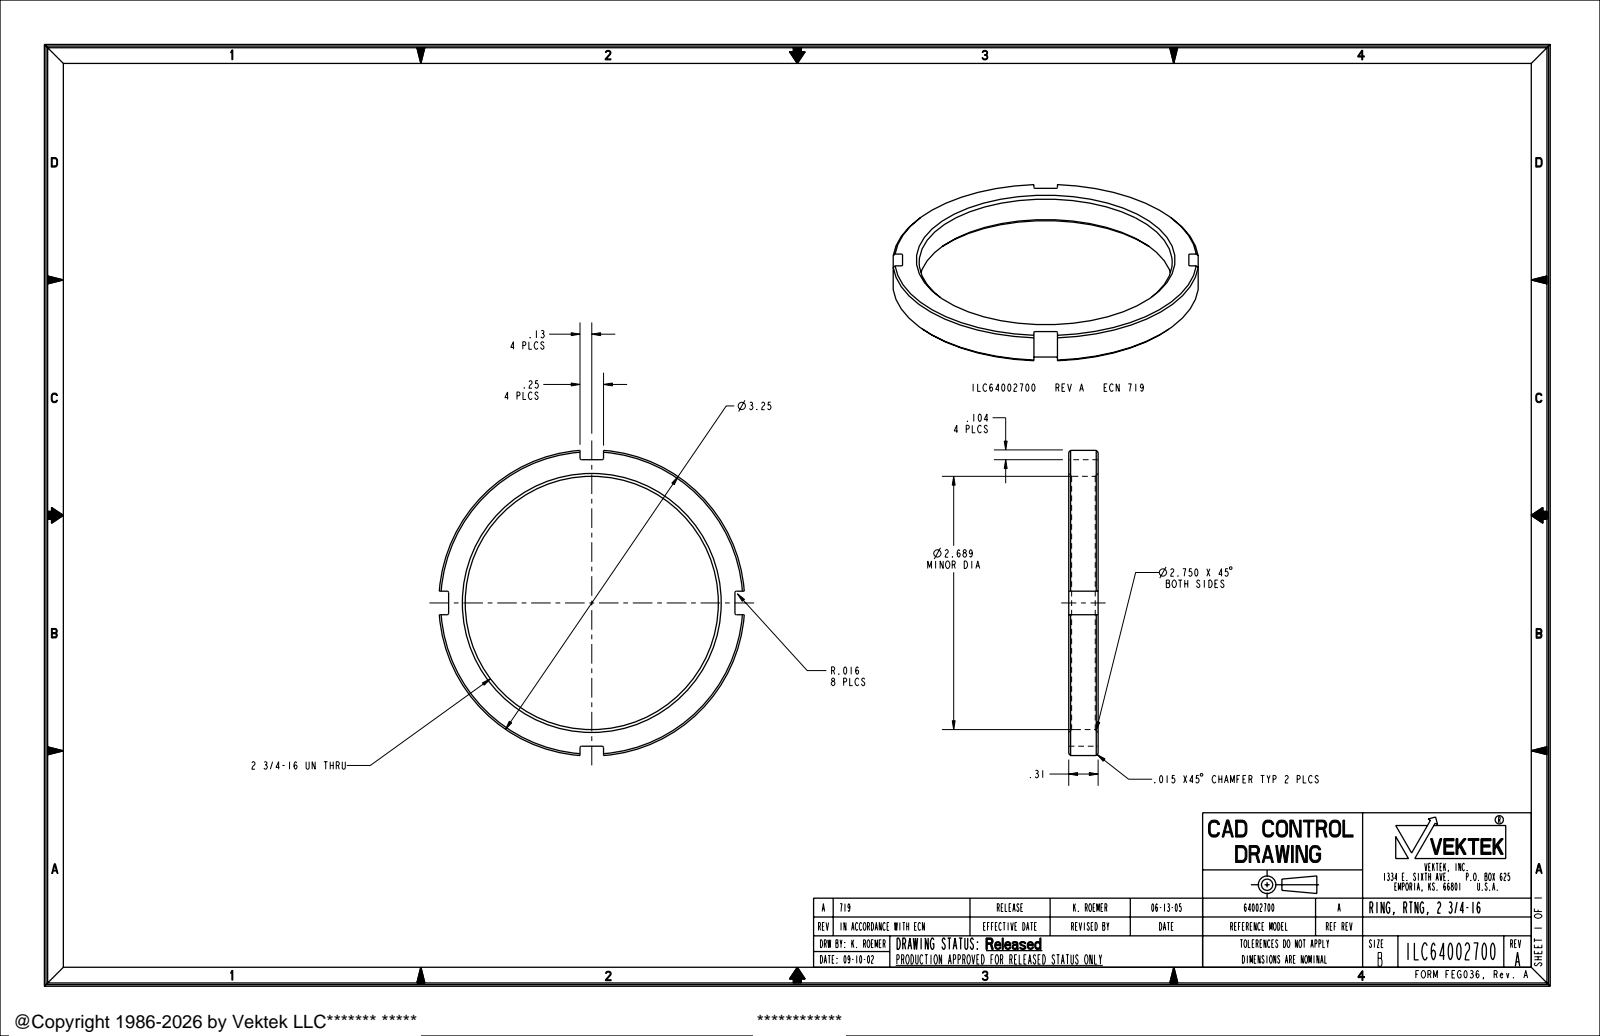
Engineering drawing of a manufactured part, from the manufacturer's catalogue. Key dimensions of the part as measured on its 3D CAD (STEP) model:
Part name (STEP PRODUCT): ILC64002700
STEP written by: PRO/ENGINEER BY PARAMETRIC TECHNOLOGY CORPORATION, 2004290 (AUTOMOTIVE_DESIGN_CC2)
Units: inches
Bodies: 1 solid, 40 faces (14 planar, 14 cylindrical, 12 other)
Overall size (bounding box): 3.25 × 3.25 × 0.312
Volume: 0.773 in³ · Surface area: 10.56 in²
Round holes (diameter × count): ⌀2.689 ×1
Round bosses / shafts (diameter × count): ⌀3.25 ×1
Partial cylindrical surfaces — rounded edges, fillets, slot ends (radius × count): R0.016 ×8
Main face-to-face distances: 0.312, 1.396, 1.646, 3.042, 0.25
